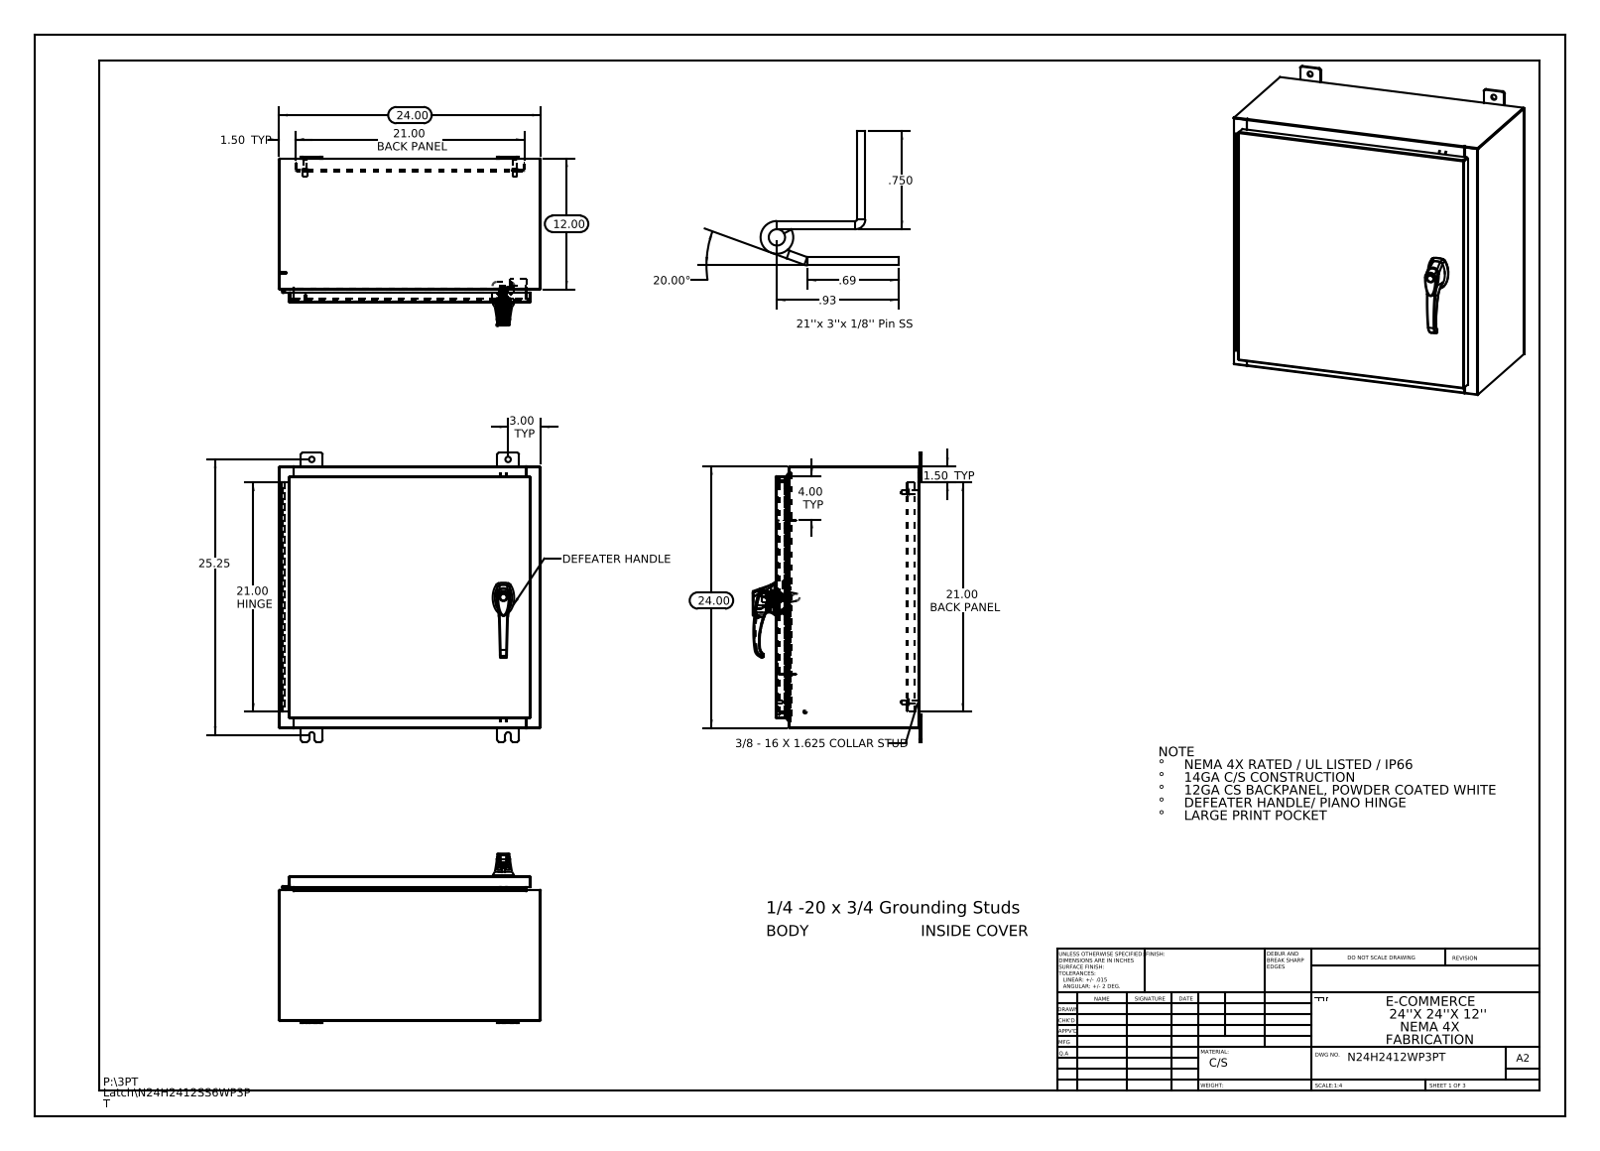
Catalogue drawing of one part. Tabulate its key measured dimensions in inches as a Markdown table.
| quantity | value |
| --- | --- |
| part name | N24H2412SS6WP3PT; 00005309_G26103101; N24H2412SS6WP3PT Hinge Enclosure Side2; 2616310101 (+8 more) |
| STEP written by | SolidWorks 2013 (CONFIG_CONTROL_DESIGN) |
| units | inches |
| bodies | 31 solids, 2412 faces (865 planar, 893 cylindrical, 654 other) |
| overall size | 26.5 × 24 × 15.495 |
| volume | 251.8 in³ |
| surface area | 6 285 in² |
| round holes (diameter × count) | 0.5 × 8, 0.25 × 4, 0.138 × 3, 0.161 × 3, 0.079 × 2, 0.203 × 2, 0.313 × 2, 0.437 × 2, 0.125 × 1, 0.125 × 1, 0.197 × 1, 0.276 × 1 |
| round bosses / shafts (diameter × count) | 0.625 × 4, 0.375 × 4, 0.33 × 4, 1.181 × 1, 0.748 × 1, 0.68 × 1, 0.661 × 1, 0.639 × 1 |
| partial cylindrical surfaces (radius × count) | 0.118 × 37, 0.006 × 33, 0.19 × 24, 0.013 × 22, 0.088 × 18, 0.039 × 15, 0.028 × 12, 0.008 × 6 |
| main face-to-face distances | 0.075, 23.925, 13.126, 23.85, 24, 13.051, 13.201, 0.104, 1, 1.075 |
| hole center spacings | 7.68, 0.295, 0.625, 0.841, 1.25, 1.313, 1.561, 1.858 |
